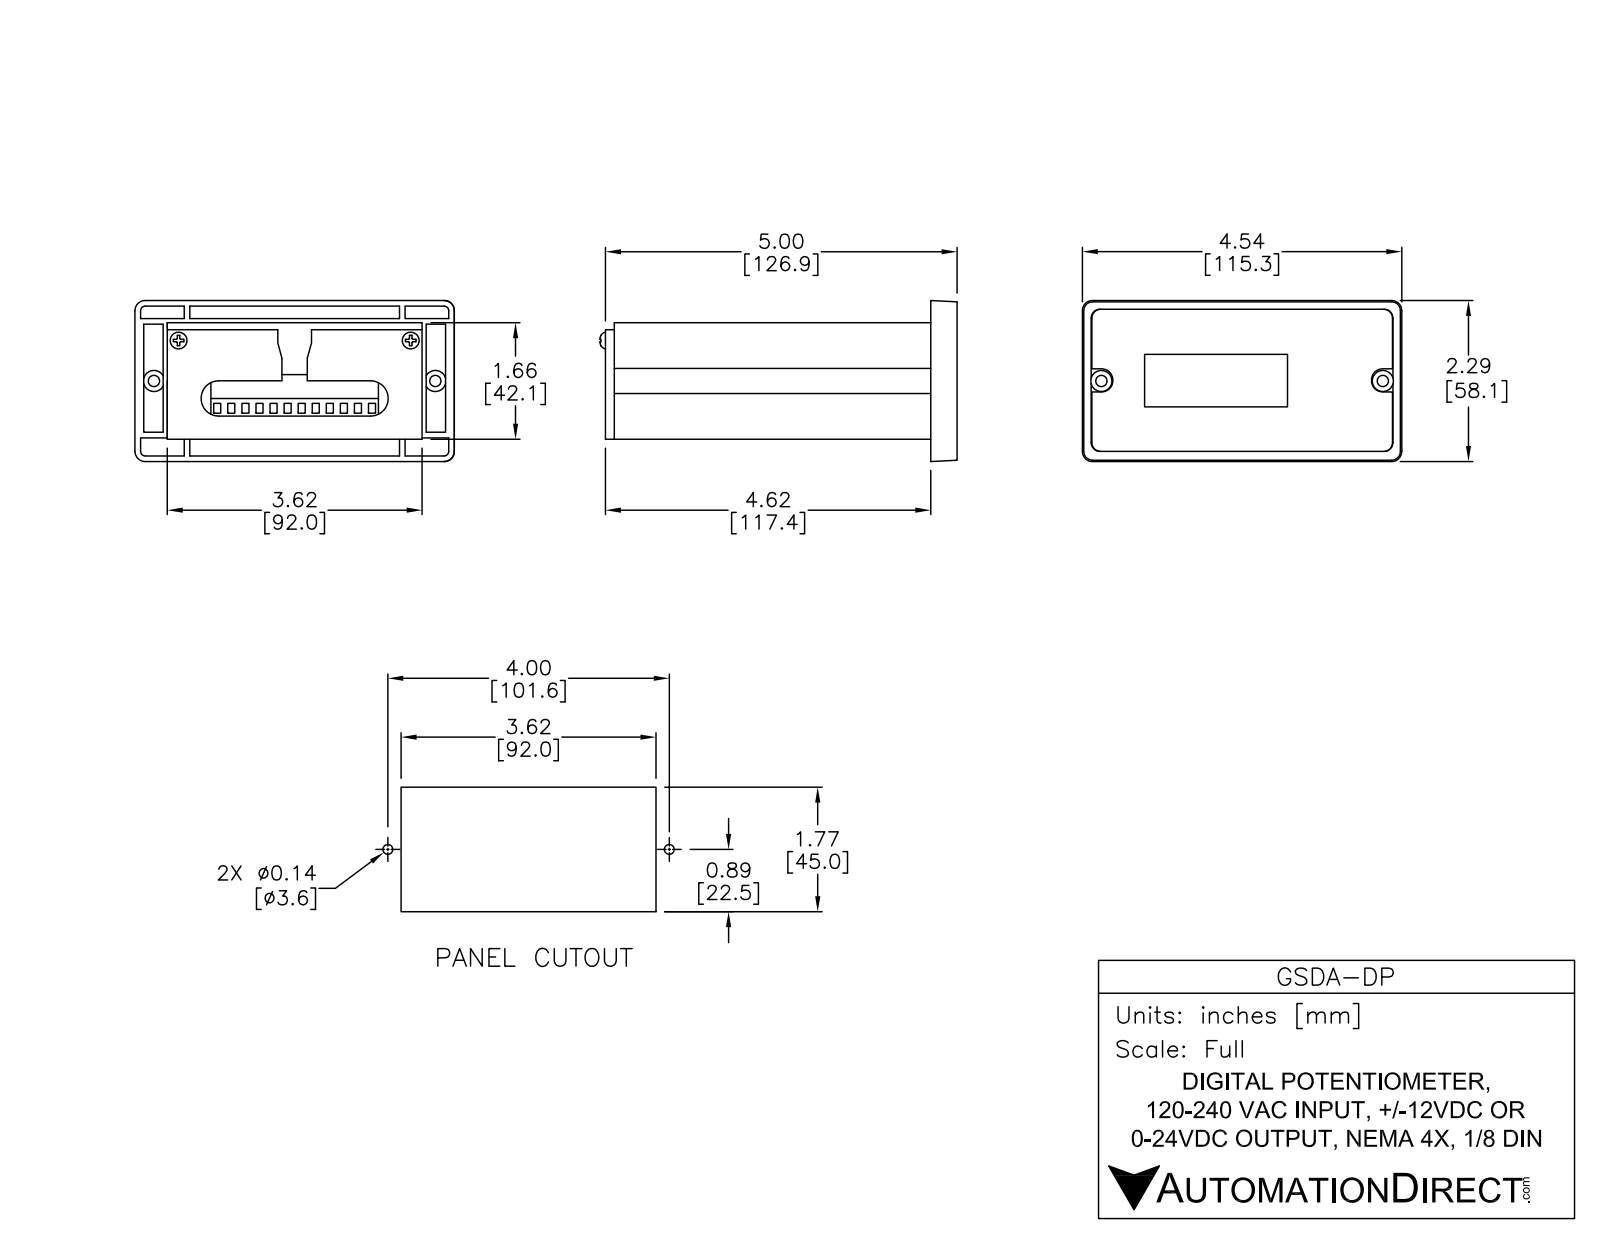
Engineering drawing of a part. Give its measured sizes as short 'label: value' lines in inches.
name: LX22; HDR11; 0805_CAP_2; DIOM_SMA (+8 more)
written by: SolidWorks 2014 (AUTOMOTIVE_DESIGN)
unit: in
bodies: 667 solids, 10734 faces (7071 planar, 3370 cylindrical, 293 other)
size: 5.038 × 4.539 × 2.289
volume: 11.43 in³; area: 288.6 in²
holes: 77× ⌀0.04, 38× ⌀0.033, 30× ⌀0.035, 20× ⌀0.02, 17× ⌀0.055, 12× ⌀0.055, 12× ⌀0.157, 10× ⌀0.046, 8× ⌀0.043, 6× ⌀0.059, 6× ⌀0.147, 6× ⌀0.16
bosses: 40× ⌀0.02, 12× ⌀0.038, 11× ⌀0.134, 10× ⌀0.033, 10× ⌀0.027, 8× ⌀0.075, 8× ⌀0.028, 6× ⌀0.413
rounds: 130× R0.006, 88× R0.004, 64× R0.004, 21× R0.05, 16× R0.004, 16× R0.006, 16× R0.012, 16× R0.039
face distances: 0.045, 0.064, 1.267, 1.52, 1.565, 1.202, 0.099, 1.422, 1.467, 0.318
hole spacings: 0.1, 0.2, 0.3, 0.4, 0.5, 0.197, 1.076, 0.535
